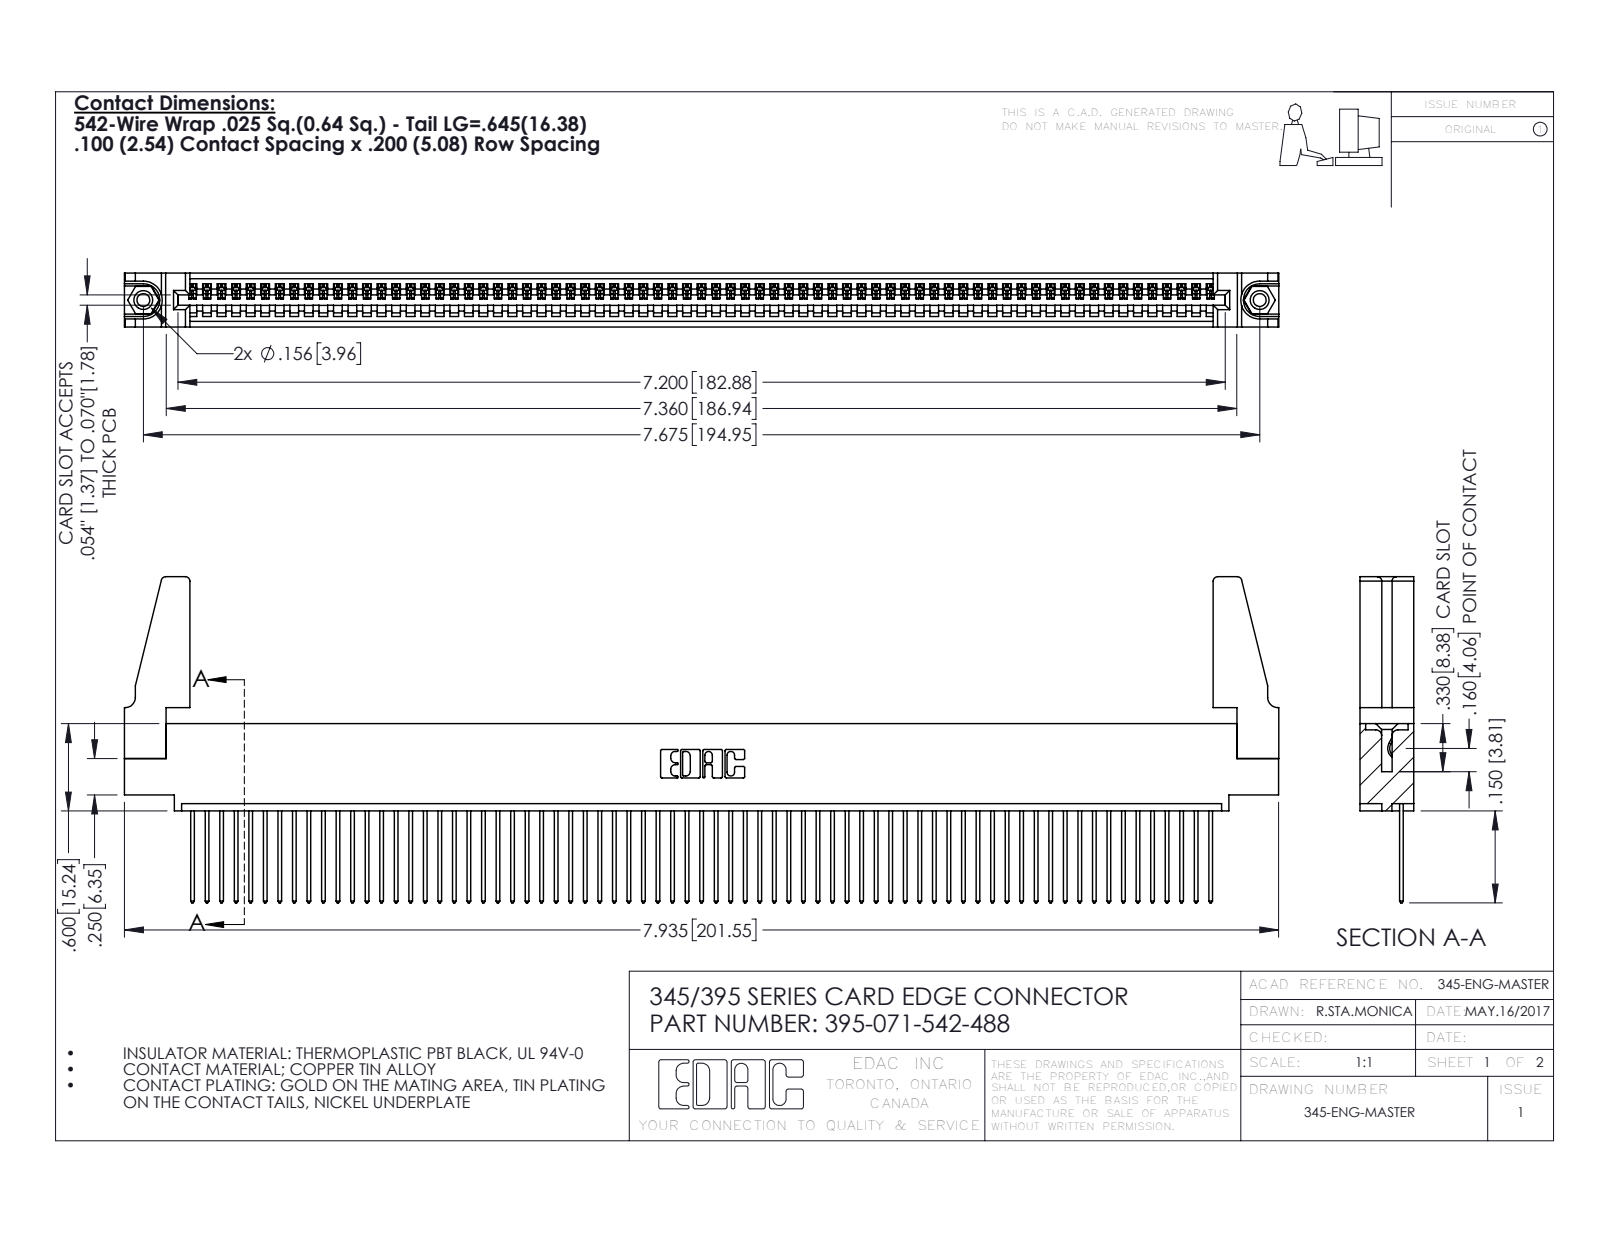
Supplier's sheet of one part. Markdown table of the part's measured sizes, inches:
| quantity | value |
| --- | --- |
| part name | 345-292-001_345-293-142; 395-071-542-488; 345-220-078_345-220-088; 345 Part_0.110 Offset - 0.156 Dia-TH (+1 more) |
| STEP written by | SolidWorks 2016 (CONFIG_CONTROL_DESIGN) |
| units | inches |
| bodies | 76 solids, 4372 faces (2996 planar, 1360 cylindrical, 16 other) |
| overall size | 7.936 × 2.242 × 0.37 |
| volume | 1.386 in³ |
| surface area | 47.24 in² |
| round holes (diameter × count) | 0.089 × 2, 0.125 × 2, 0.156 × 2, 0.064 × 1 |
| round bosses / shafts (diameter × count) | 0.155 × 2 |
| partial cylindrical surfaces (radius × count) | 0.006 × 142, 0.01 × 142, 0.01 × 22, 0.03 × 8, 0.007 × 6, 0.031 × 6, 0.026 × 3, 0.031 × 2 |
| main face-to-face distances | 0.072, 0.298, 0.37, 0.098, 0.272, 0.025, 0.2, 0.225, 0.149, 0.072 |
| hole center spacings | 0.27, 7.439, 7.675 |
